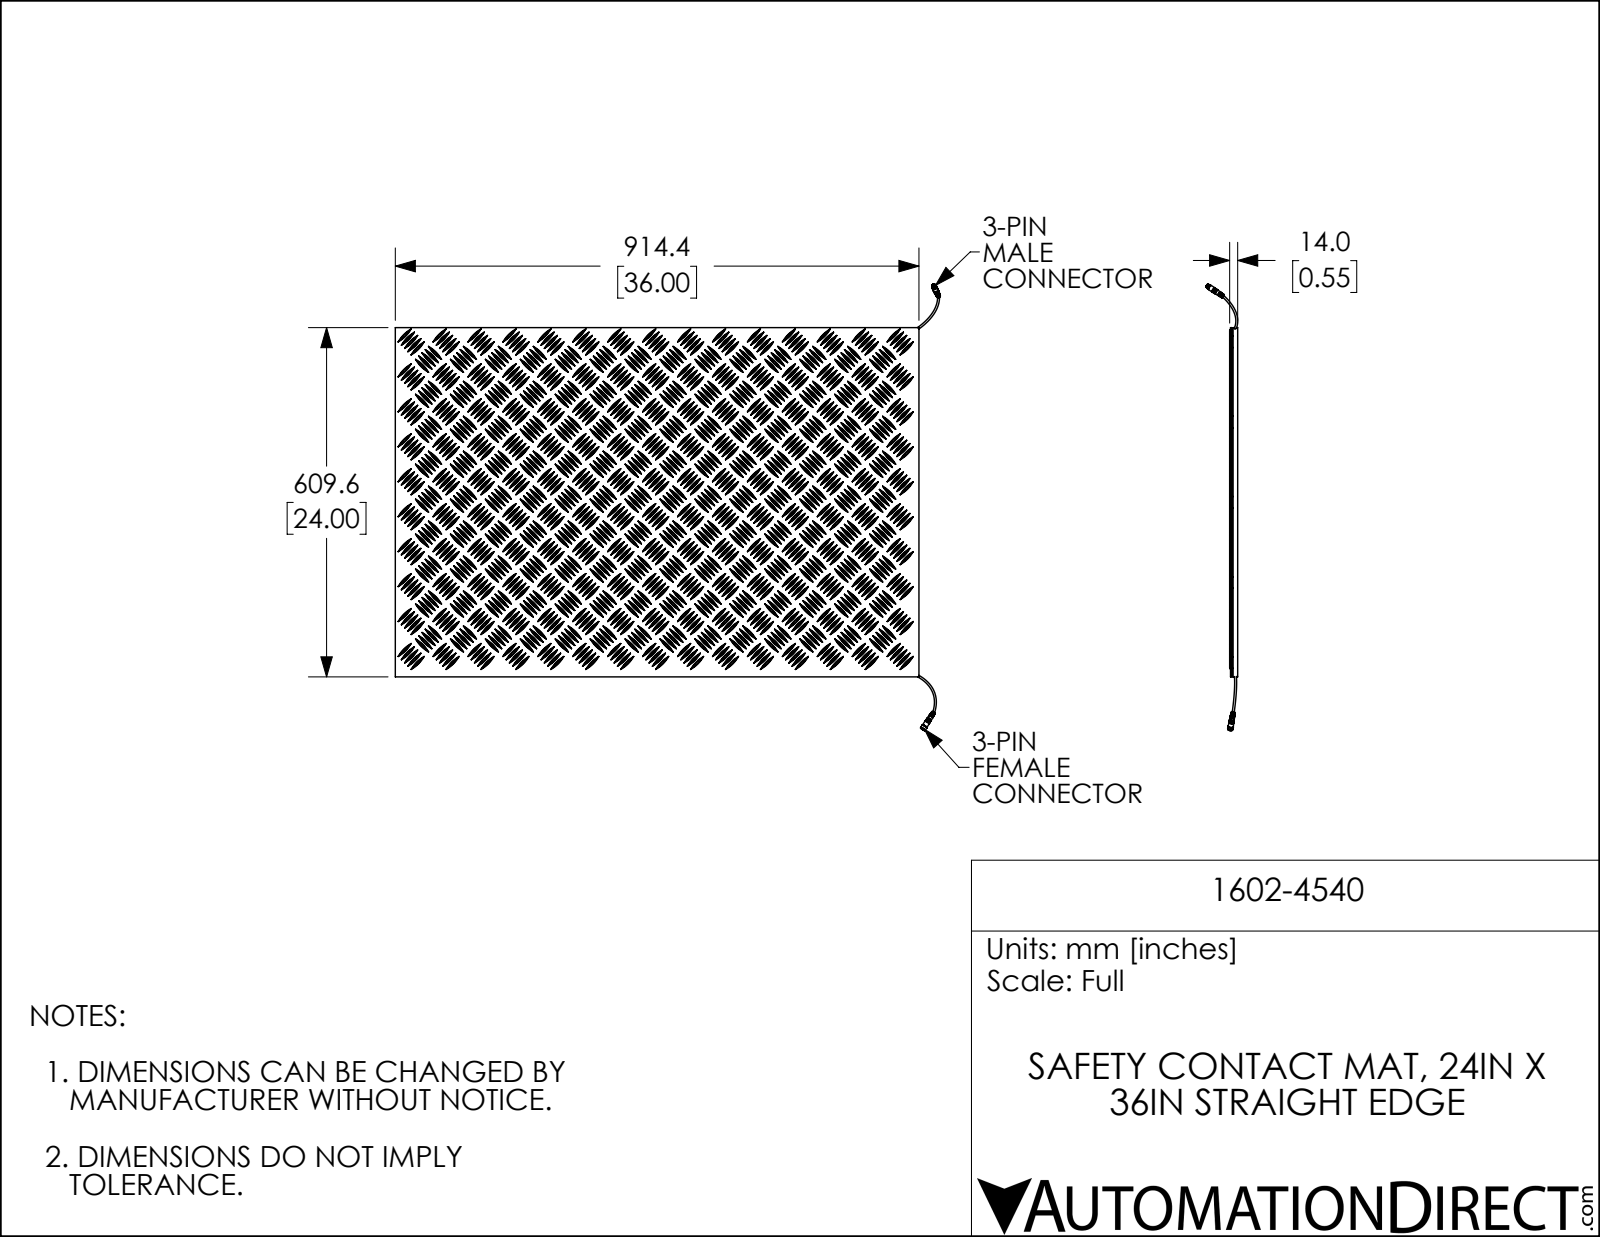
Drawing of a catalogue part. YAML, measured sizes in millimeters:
part_name: "1602-4540"
step_written_by: "SolidWorks 2018 (AUTOMOTIVE_DESIGN)"
units: millimeters
bodies: {solids: 47, faces: 4431, planar: 1556, cylindrical: 60, other: 2815}
overall_size: [951.9, 779.7, 55.8]
volume: 6024000
surface_area: 2363000
round_holes:
  - {diameter: 1.6, count: 3}
  - {diameter: 3.4, count: 2}
  - {diameter: 5.8, count: 1}
  - {diameter: 5.9, count: 1}
  - {diameter: 6.9, count: 1}
  - {diameter: 7.2, count: 1}
round_bosses_or_shafts:
  - {diameter: 20, count: 35}
  - {diameter: 1, count: 3}
  - {diameter: 8.8, count: 2}
  - {diameter: 5.7, count: 2}
  - {diameter: 9.6, count: 1}
  - {diameter: 9, count: 1}
  - {diameter: 8, count: 1}
  - {diameter: 7, count: 1}
face_to_face_distances: [2, 10, 8, 12.5, 4.5, 2.5, 1.5, 6, 14, 4]
hole_center_spacings: [1.8, 2.5, 1.8, 3.5]
